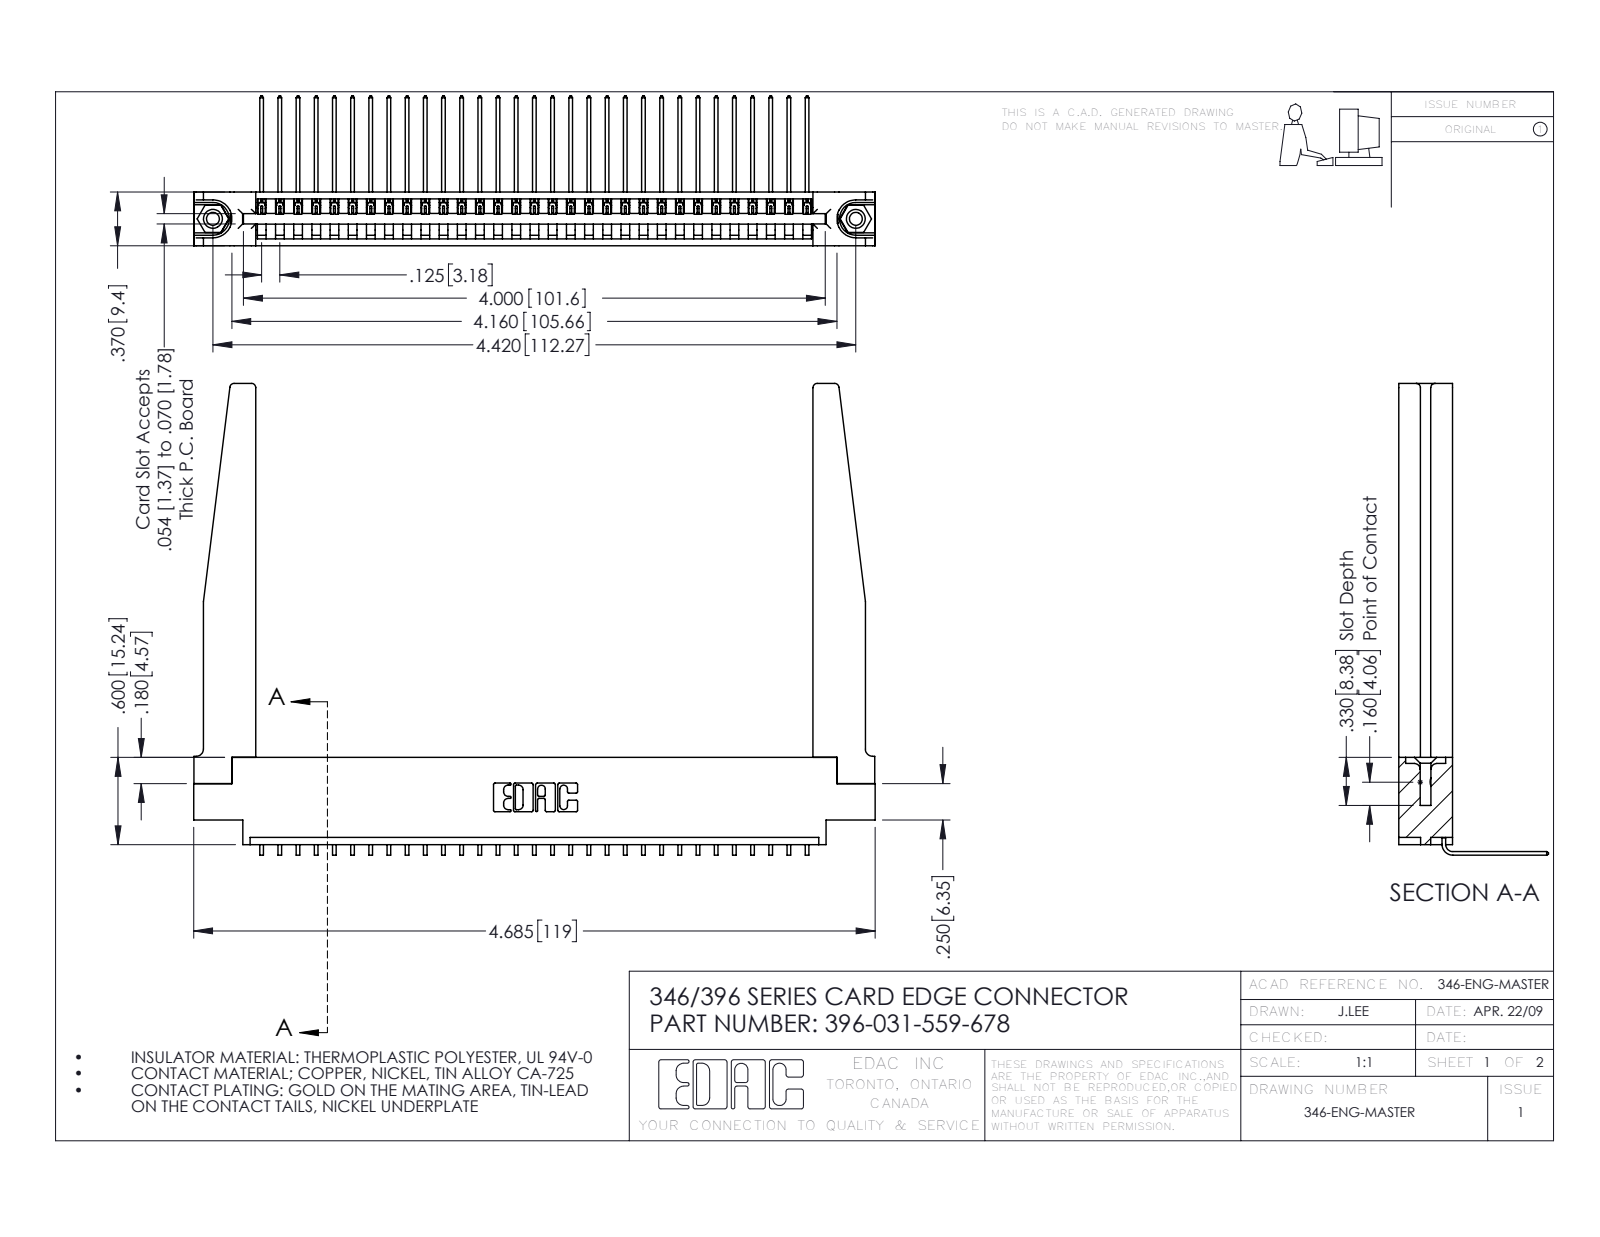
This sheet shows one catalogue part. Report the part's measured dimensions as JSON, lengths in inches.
{"part_name": "346-220-078_345-220-078; 345-250-001_345-250-001-102; 345-292-001_558 559 Tail - 1; 346 Part_0.170 Offset - 0.156 Dia-TH (+1 more)", "step_written_by": "SolidWorks 2016 (CONFIG_CONTROL_DESIGN)", "units": "inches", "bodies": {"solids": 36, "faces": 2220, "planar": 1524, "cylindrical": 644, "other": 52}, "overall_size": [4.685, 3.243, 1.03], "volume_in3": 1.109, "surface_area_in2": 32.98, "round_holes": [[0.089, 2], [0.125, 2], [0.156, 2], [0.064, 1]], "round_bosses_or_shafts": [[0.155, 2]], "partial_cylinders_radius": [[0.006, 62], [0.01, 22], [0.03, 8], [0.007, 6], [0.031, 6], [0.026, 3], [0.05, 3], [0.031, 2]], "face_to_face_distances": [0.37, 0.048, 0.322, 0.072, 0.148, 0.15, 0.025, 0.25, 0.298, 0.222], "hole_center_spacings": [0.246, 4.212, 4.42]}
